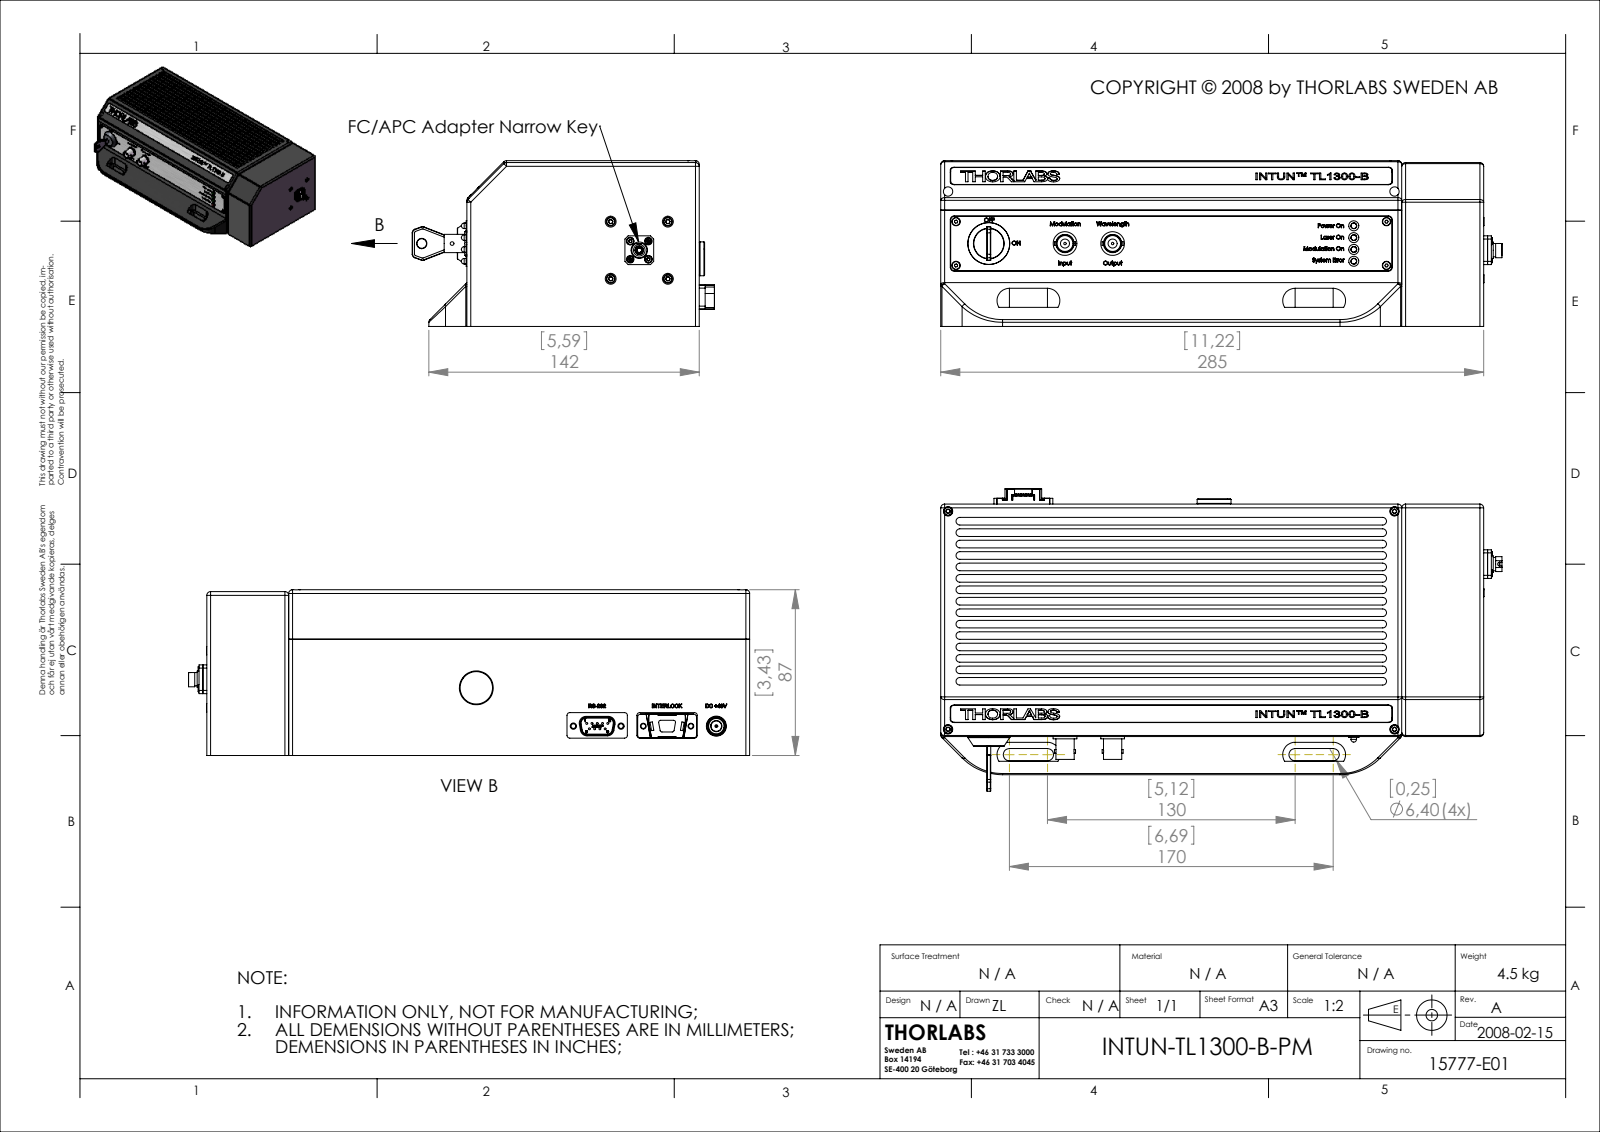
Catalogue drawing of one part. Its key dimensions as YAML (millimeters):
part_name: "INTUN-TL1300-B-PM"
step_written_by: "SolidWorks 2007 (CONFIG_CONTROL_DESIGN)"
units: millimeters
bodies: {solids: 0, faces: 3674, planar: 1985, cylindrical: 777, other: 912}
overall_size: [294.61, 158.68, 87]
round_holes:
  - {diameter: 1.02, count: 9}
  - {diameter: 1.6, count: 8}
  - {diameter: 2.05, count: 7}
  - {diameter: 2.22, count: 4}
  - {diameter: 2.26, count: 4}
  - {diameter: 2.4, count: 4}
  - {diameter: 2.5, count: 4}
  - {diameter: 2.9, count: 4}
  - {diameter: 3, count: 4}
  - {diameter: 3.05, count: 4}
  - {diameter: 3.2, count: 4}
  - {diameter: 3.99, count: 4}
round_bosses_or_shafts:
  - {diameter: 4.5, count: 9}
  - {diameter: 2.5, count: 9}
  - {diameter: 1.02, count: 9}
  - {diameter: 2, count: 6}
  - {diameter: 6.2, count: 4}
  - {diameter: 5.3, count: 4}
  - {diameter: 4.7, count: 4}
  - {diameter: 4.25, count: 4}
partial_cylinders:
  - {radius: 2, count: 79}
  - {radius: 5, count: 18}
  - {radius: 1.57, count: 16}
  - {radius: 0.2, count: 14}
  - {radius: 1.02, count: 10}
  - {radius: 3.5, count: 10}
  - {radius: 6, count: 10}
  - {radius: 0.71, count: 9}
face_to_face_distances: [6, 2, 5.6, 6.25, 77.75, 72.15, 116, 1, 83, 77.4]
hole_center_spacings: [9.51, 22.25, 22.26, 23, 2.77, 6.72, 6.73, 9.5]
